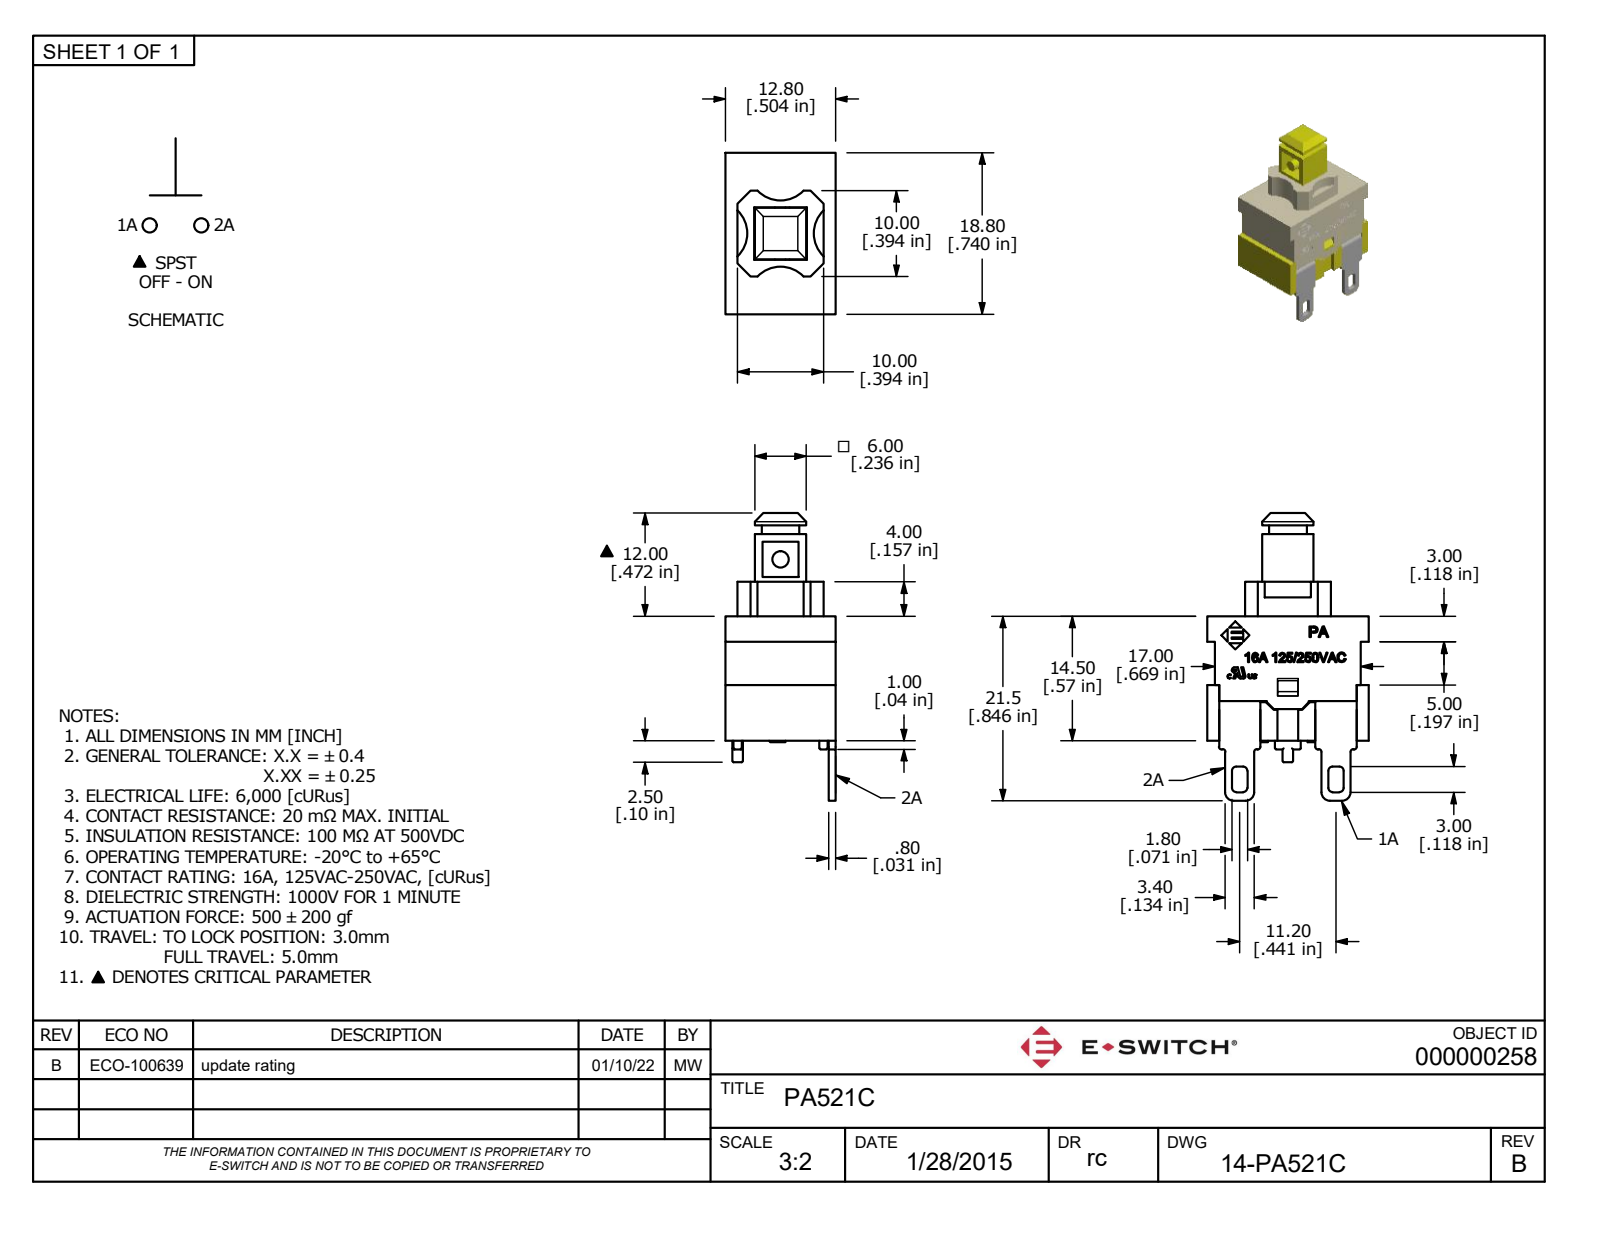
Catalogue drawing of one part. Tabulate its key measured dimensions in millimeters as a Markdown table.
| quantity | value |
| --- | --- |
| part name | PA521C |
| STEP written by | Autodesk Inventor 2022 (AUTOMOTIVE_DESIGN) |
| units | millimeters |
| bodies | 1 solid, 779 faces (566 planar, 83 cylindrical, 130 other) |
| overall size | 33.5 × 18.8 × 12.8 |
| volume | 2 128 mm³ |
| surface area | 4 272 mm² |
| round holes (diameter × count) | 3 × 1 |
| round bosses / shafts (diameter × count) | 0.95 × 4, 2.5 × 1, 1.9 × 1 |
| partial cylindrical surfaces (radius × count) | 0.12 × 16, 0.25 × 16, 0.5 × 9, 0.15 × 8, 0.3 × 8, 1 × 6, 3.71 × 4, 1.72 × 1 |
| main face-to-face distances | 0.8, 12, 0.9, 16.8, 2, 8.6, 4.4, 1.1, 12.8, 5.15 |
